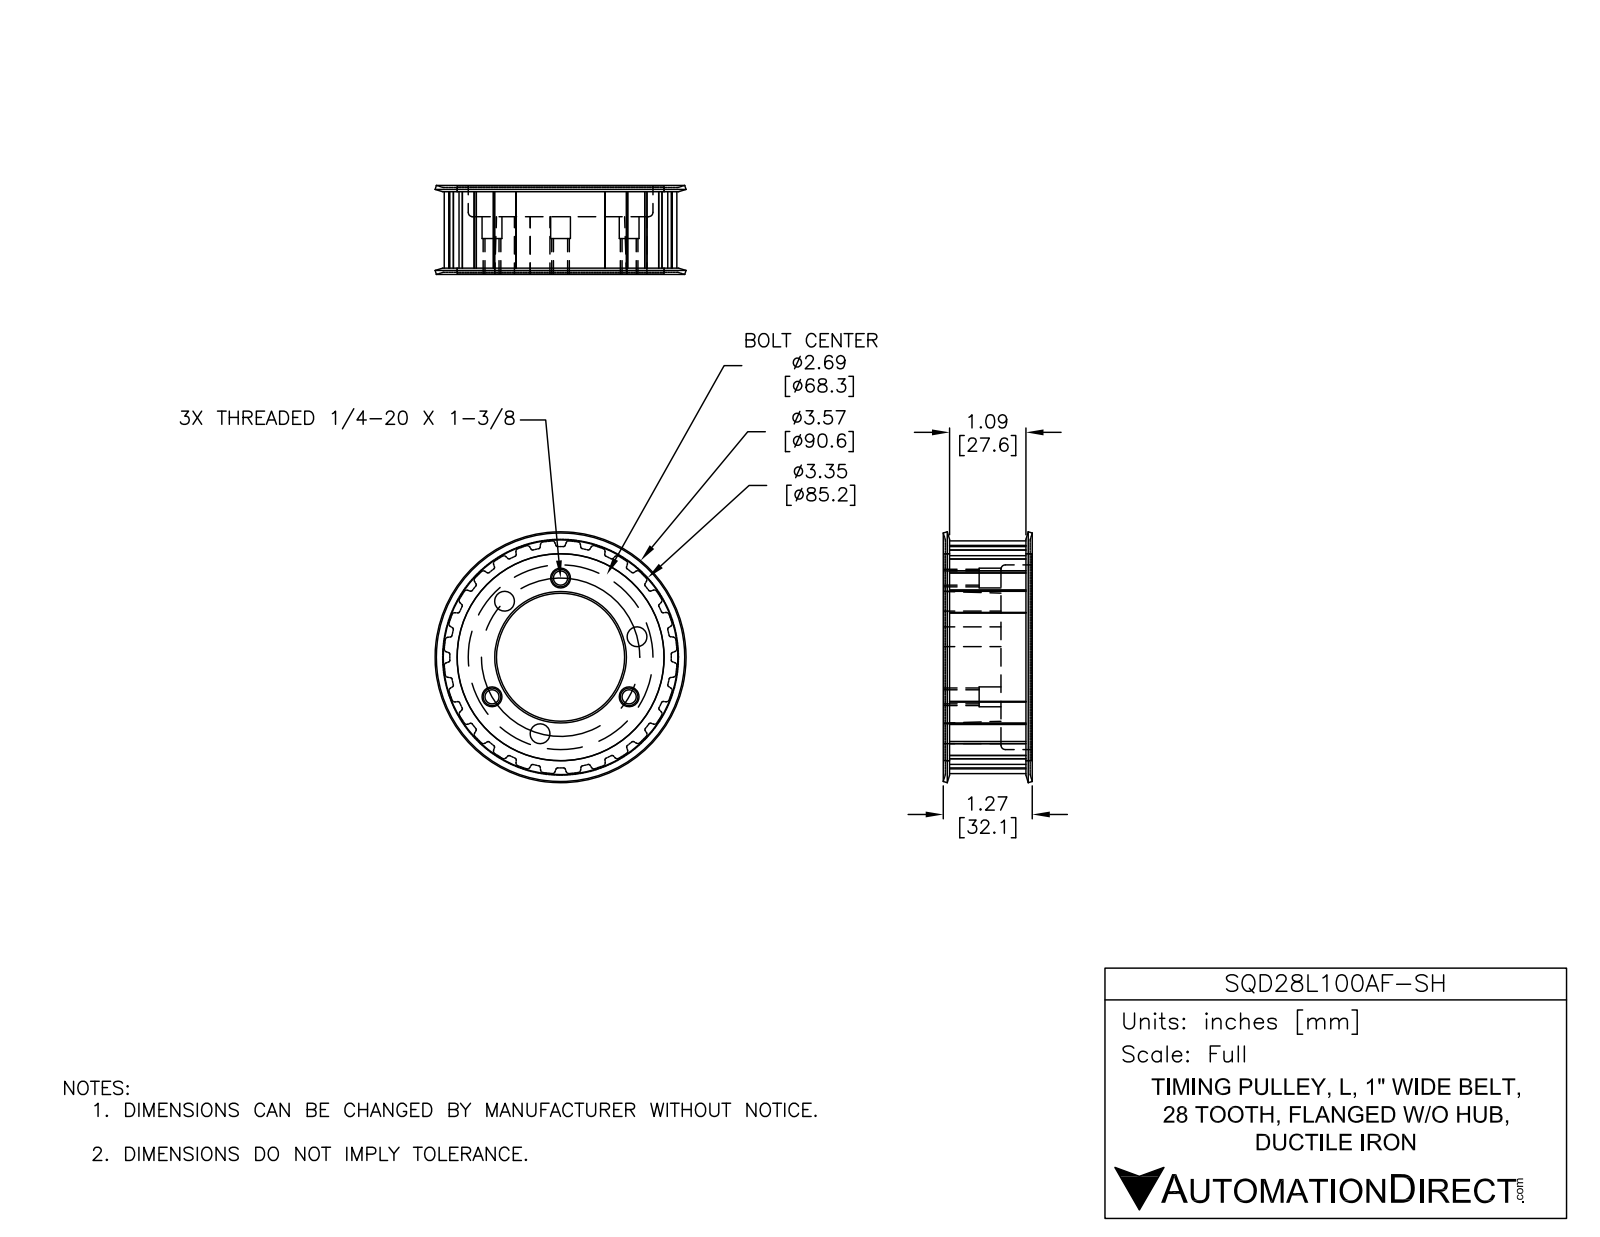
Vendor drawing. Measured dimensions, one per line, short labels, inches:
name: SQD28L100AF-SH
written by: SolidWorks 2018 (AUTOMOTIVE_DESIGN)
unit: in
bodies: 1 solid, 303 faces (96 planar, 191 cylindrical, 16 other)
size: 3.566 × 3.566 × 1.265
volume: 5.675 in³; area: 47.33 in²
holes: 6× ⌀0.281, 3× ⌀0.201, 1× ⌀2.625, 1× ⌀2.942
bosses: 1× ⌀2.939
rounds: 56× R0.021, 56× R0.04, 1× R1.657
face distances: 0.022, 1.228, 0.813, 0.415, 1.205, 0.79, 0.437, 1.25, 0.082, 0.06
hole spacings: 1.125, 1.948, 2.231, 0.861, 0.861, 0.861, 1.125, 1.369
